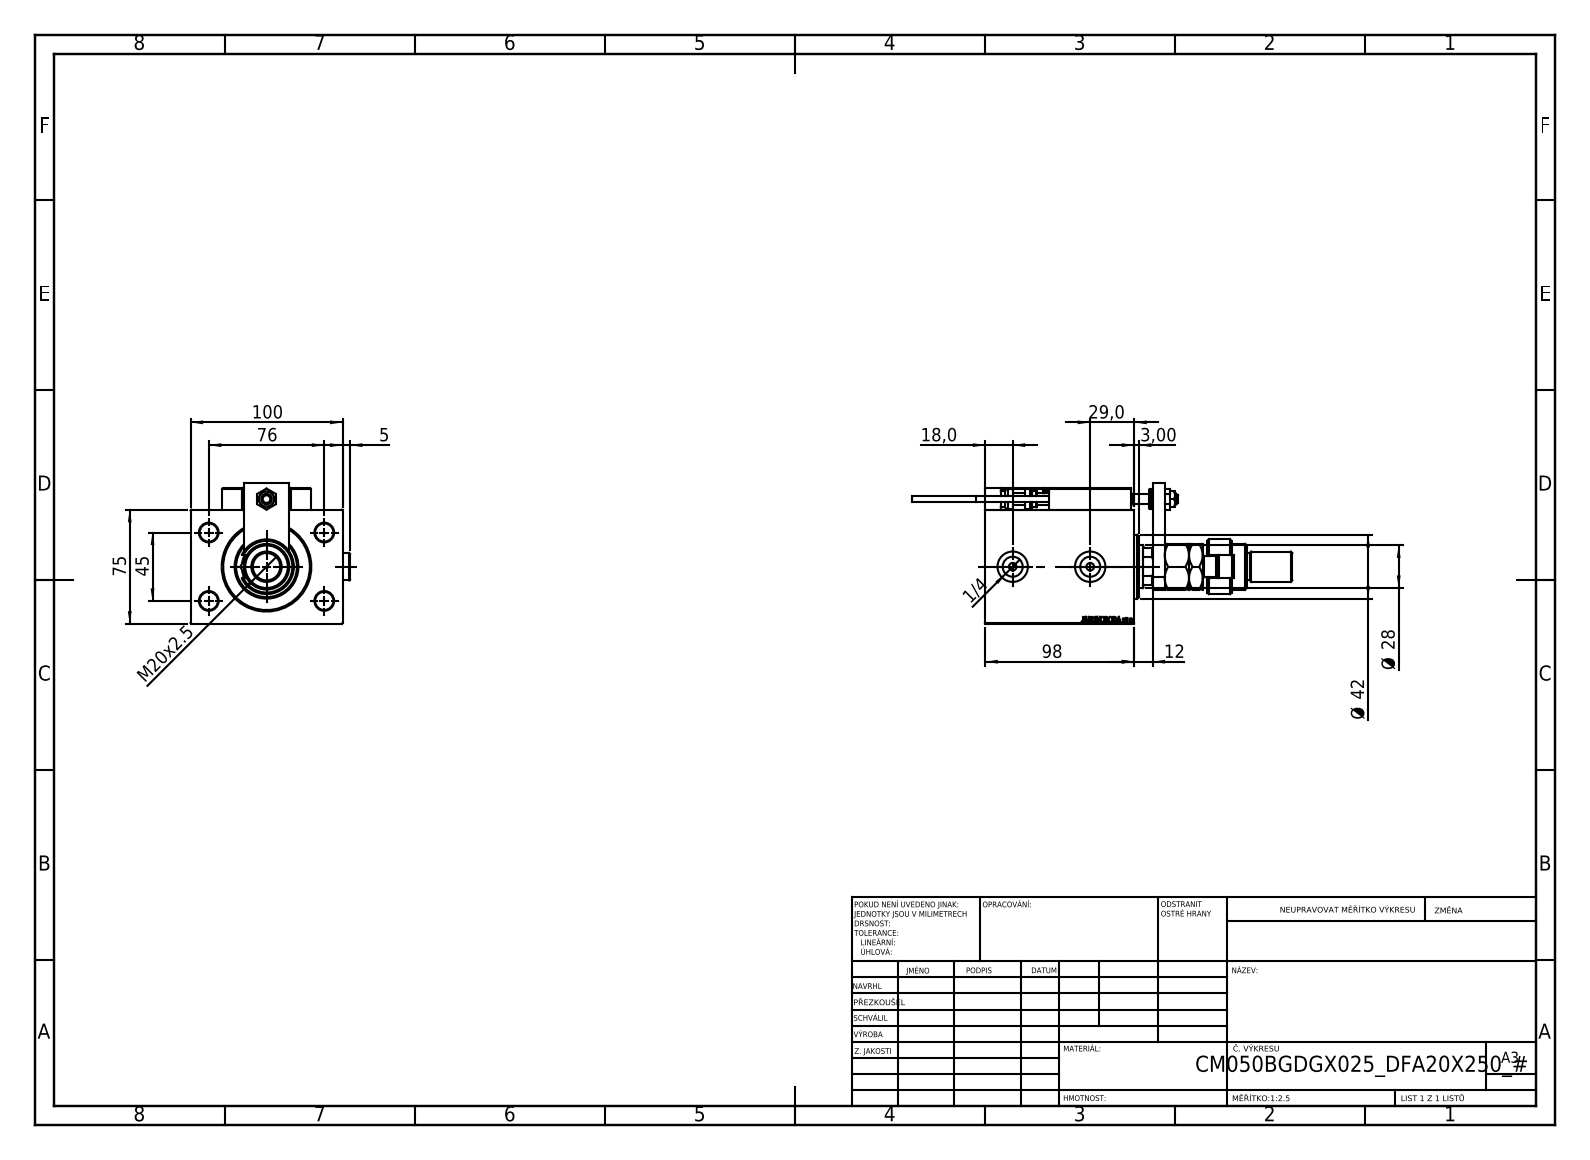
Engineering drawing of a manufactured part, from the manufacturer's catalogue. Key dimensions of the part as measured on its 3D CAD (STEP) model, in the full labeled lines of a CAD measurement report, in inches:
Part name (STEP PRODUCT): KONCOVKA; ALLEN BOLT D8; ALLEN BOLT D5; TYC_L79 (+7 more)
STEP written by: SolidWorks 2019 (CONFIG_CONTROL_DESIGN)
Units: inches
Bodies: 28 solids, 1460 faces (624 planar, 215 cylindrical, 621 other)
Overall size (bounding box): 9.843 × 4.13 × 3.642
Volume: 47.73 in³ · Surface area: 213.8 in²
Round holes (diameter × count): ⌀0.315 ×5, ⌀0.126 ×4, ⌀0.157 ×4, ⌀0.197 ×4, ⌀0.472 ×4, ⌀0.787 ×3, ⌀0.518 ×2, ⌀0.276 ×1, ⌀0.728 ×1, ⌀1.102 ×1, ⌀1.24 ×1, ⌀1.28 ×1
Round bosses / shafts (diameter × count): ⌀0.709 ×3, ⌀0.197 ×2, ⌀0.15 ×2, ⌀1.654 ×1, ⌀1.417 ×1, ⌀1.181 ×1, ⌀0.866 ×1, ⌀0.551 ×1
Partial cylindrical surfaces — rounded edges, fillets, slot ends (radius × count): R0.012 ×30, R0.118 ×2, R0.295 ×1, R0.472 ×1, R0.531 ×1
Main face-to-face distances: 2.953, 0.551, 3.937, 3.858, 0.472, 3.307, 1.26, 0.787, 0.984, 3.386
Hole centre spacings: 1.739, 0.448, 0.787, 1.165, 1.169, 1.42, 1.661, 1.729
